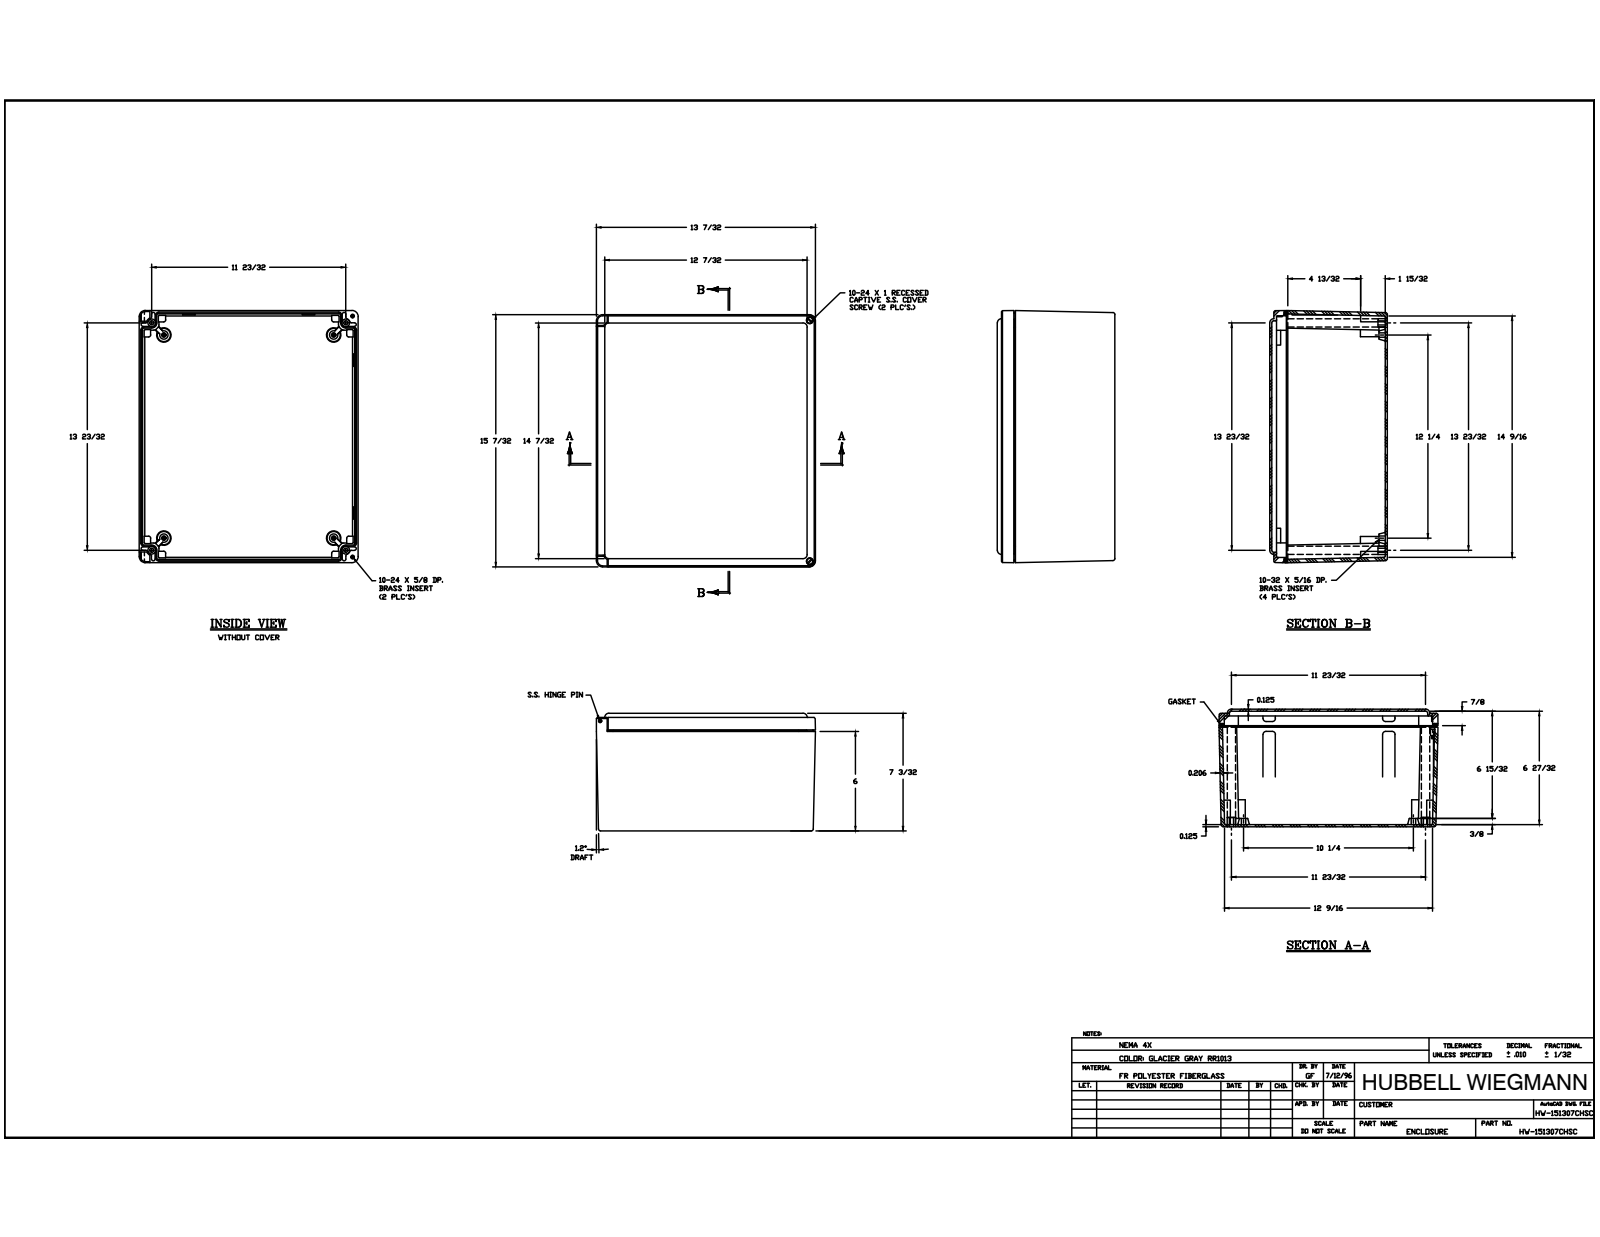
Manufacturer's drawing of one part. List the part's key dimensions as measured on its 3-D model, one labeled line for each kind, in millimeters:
Part name (STEP PRODUCT): WP1513HWBOX; 0.3125-18 X 0.563 DP BRASS INSERT; 10-32 X0.3125 DP BRASS INSERT; 10-24 X 0.625 DP BRASS INSERT (+8 more)
STEP written by: Autodesk Inventor 2014 (AUTOMOTIVE_DESIGN)
Units: millimetres
Bodies: 24 solids, 1049 faces (412 planar, 305 cylindrical, 332 other)
Overall size (bounding box): 386.59 × 335.8 × 180.18
Volume: 2 276 000 mm³ · Surface area: 1 082 000 mm²
Round holes (diameter × count): ⌀7.14 ×6, ⌀3.96 ×4, ⌀7.94 ×4, ⌀13.49 ×4, ⌀2.44 ×2, ⌀3.68 ×2, ⌀3.97 ×2, ⌀4.83 ×2, ⌀5.56 ×2, ⌀5.84 ×2, ⌀7.1 ×2, ⌀10.32 ×2
Round bosses / shafts (diameter × count): ⌀9.52 ×2, ⌀9.24 ×2, ⌀5.94 ×2, ⌀4.86 ×2, ⌀2.42 ×2, ⌀9.42 ×1, ⌀4.52 ×1, ⌀2.24 ×1
Partial cylindrical surfaces — rounded edges, fillets, slot ends (radius × count): R0.79 ×60, R3.17 ×40, R1.59 ×29, R0.25 ×8, R1.5 ×8, R4.76 ×8, R4.78 ×8, R6.35 ×8
Main face-to-face distances: 3.17, 177.01, 4.72, 180.18, 173.84, 3.18, 6.35, 173.83, 170.66, 19.05
Hole centre spacings: 26.39, 279.66, 330.37, 432.04, 369.1, 13.4, 14.54, 14.55
